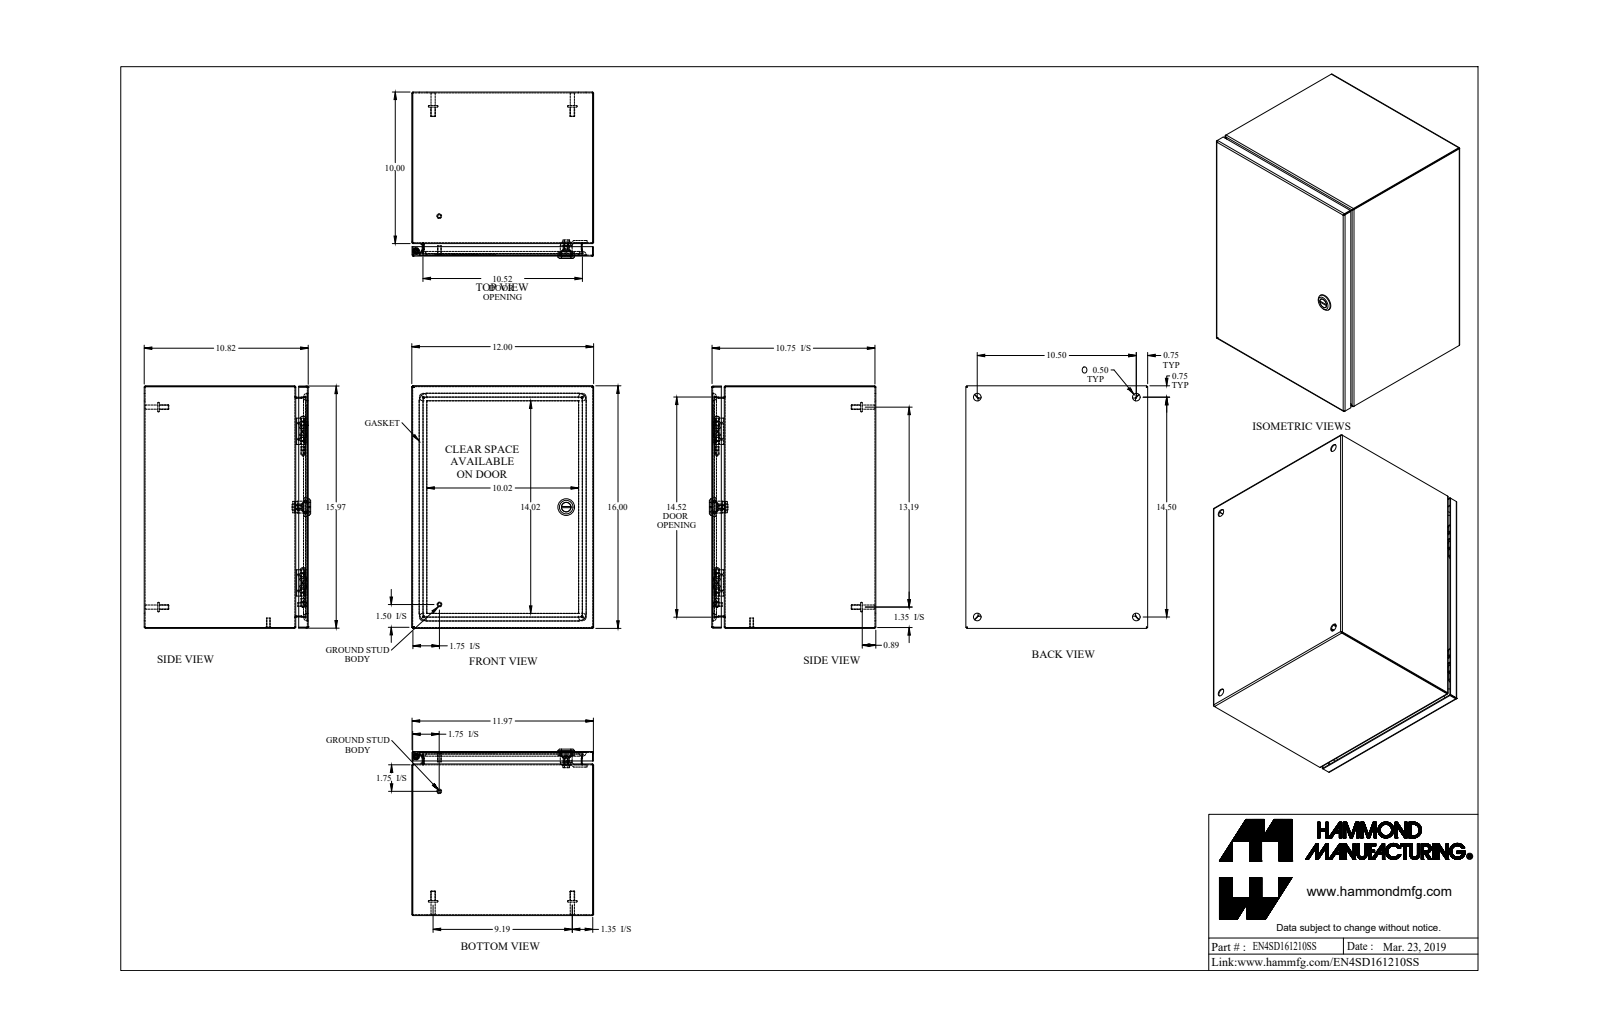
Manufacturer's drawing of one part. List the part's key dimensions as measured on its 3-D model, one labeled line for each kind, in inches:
Part name (STEP PRODUCT): EN4SD161210SS_Default
STEP written by: SolidWorks 2019 (CONFIG_CONTROL_DESIGN)
Units: inches
Bodies: 22 solids, 657 faces (303 planar, 212 cylindrical, 142 other)
Overall size (bounding box): 16 × 12 × 10.982
Volume: 65.7 in³ · Surface area: 2 234 in²
Round holes (diameter × count): ⌀0.5 ×5, ⌀0.172 ×1, ⌀0.197 ×1, ⌀0.24 ×1, ⌀0.242 ×1, ⌀0.387 ×1, ⌀0.63 ×1, ⌀0.768 ×1
Round bosses / shafts (diameter × count): ⌀0.313 ×6, ⌀0.625 ×5, ⌀0.275 ×4, ⌀0.25 ×2, ⌀1.1 ×1, ⌀0.785 ×1, ⌀0.525 ×1, ⌀0.455 ×1
Partial cylindrical surfaces — rounded edges, fillets, slot ends (radius × count): R0.029 ×21, R0.086 ×21, R0.188 ×12, R0.006 ×4, R0.062 ×4, R0.25 ×4, R0.499 ×4, R0.125 ×2
Main face-to-face distances: 0.057, 10.765, 11.943, 15.943, 10.708, 10.822, 11.886, 12, 15.886, 16
Hole centre spacings: 7.327, 10.5, 11.904, 14.5, 17.902
